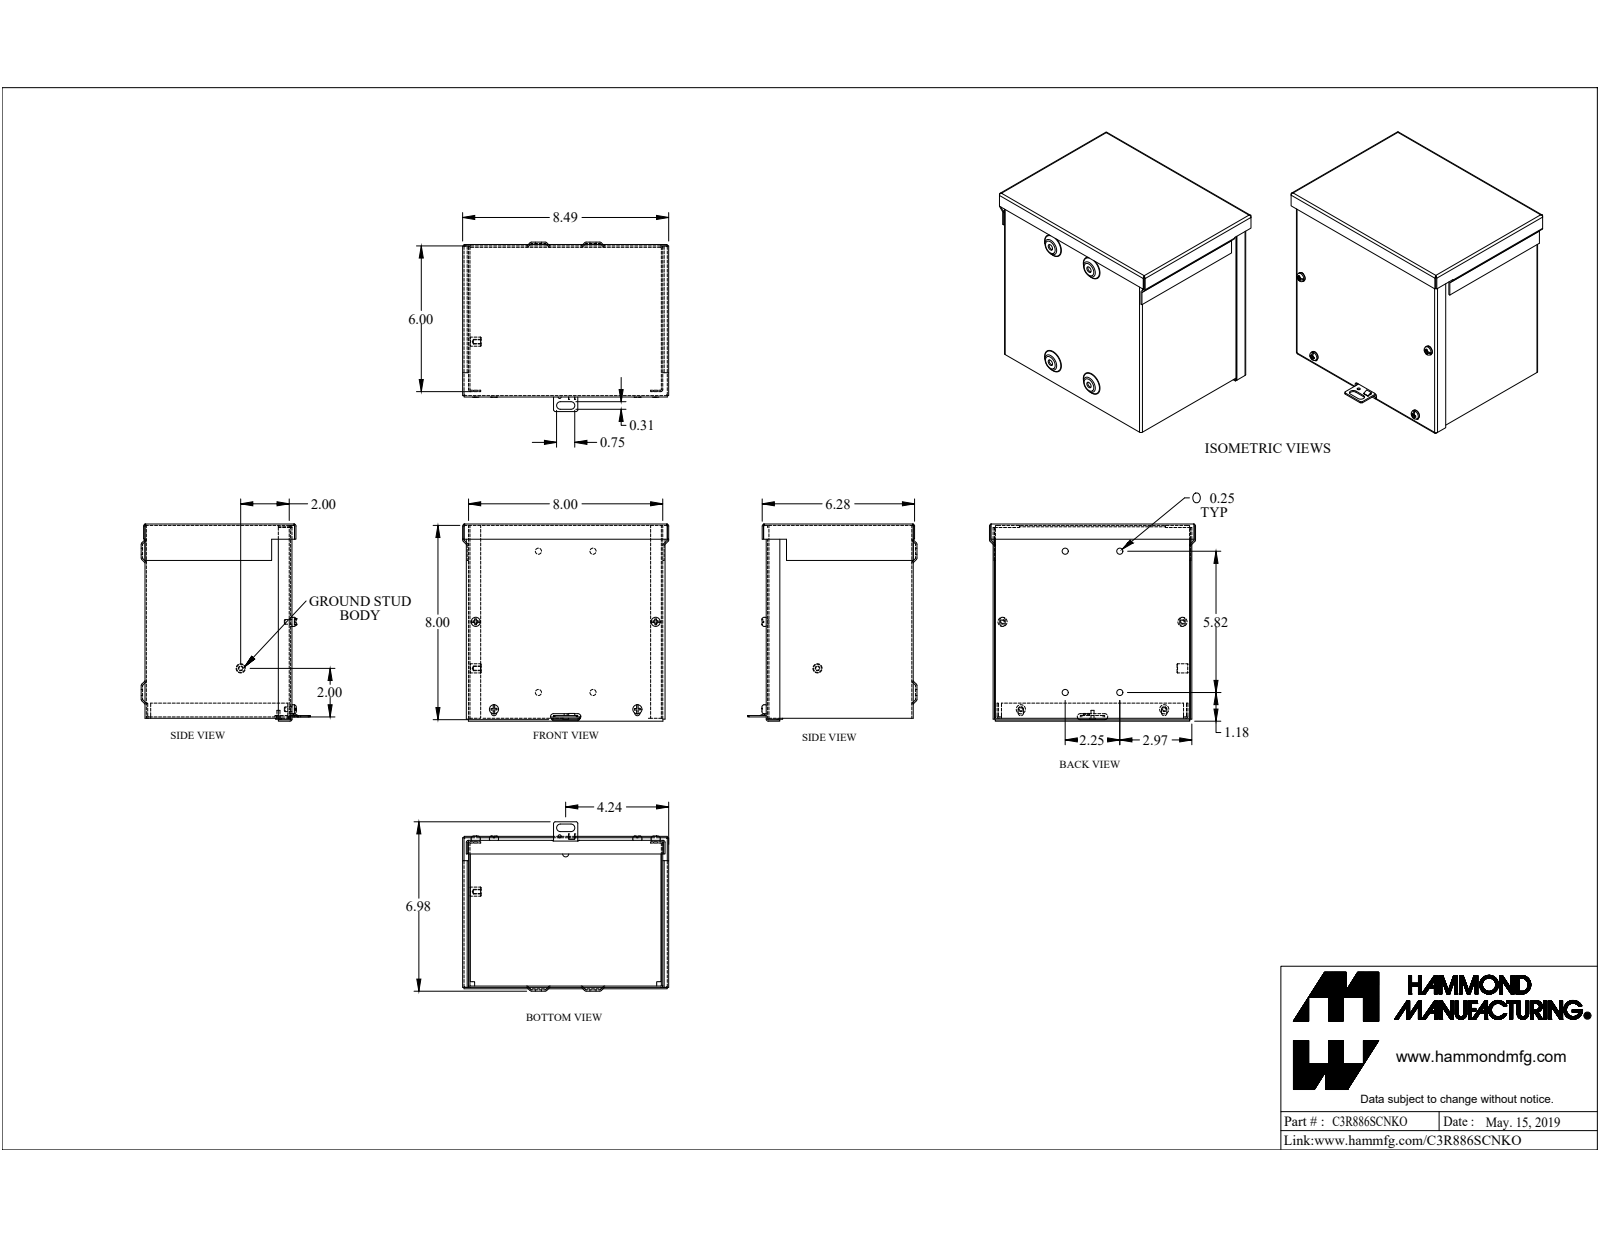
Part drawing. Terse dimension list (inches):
name: C3R886SCNKO
written by: SolidWorks 2019 (AUTOMOTIVE_DESIGN)
unit: in
bodies: 11 solids, 339 faces (211 planar, 84 cylindrical, 44 other)
size: 8.489 × 8.12 × 6.977
volume: 21.4 in³; area: 780.1 in²
holes: 4× ⌀0.17, 4× ⌀0.25, 1× ⌀0.125, 1× ⌀0.137, 1× ⌀0.156
bosses: 4× ⌀0.375, 4× ⌀0.19, 1× ⌀0.375, 1× ⌀0.125
rounds: 21× R0.029, 21× R0.086, 8× R0.109, 8× R0.125, 2× R0.156
face distances: 0.057, 7.943, 6, 8, 5.943, 0.057, 6.057, 7.886, 7.886, 7.943
hole spacings: 3.89, 5.64, 1.998, 2.25, 3.752, 4.165, 5.818, 6.238
